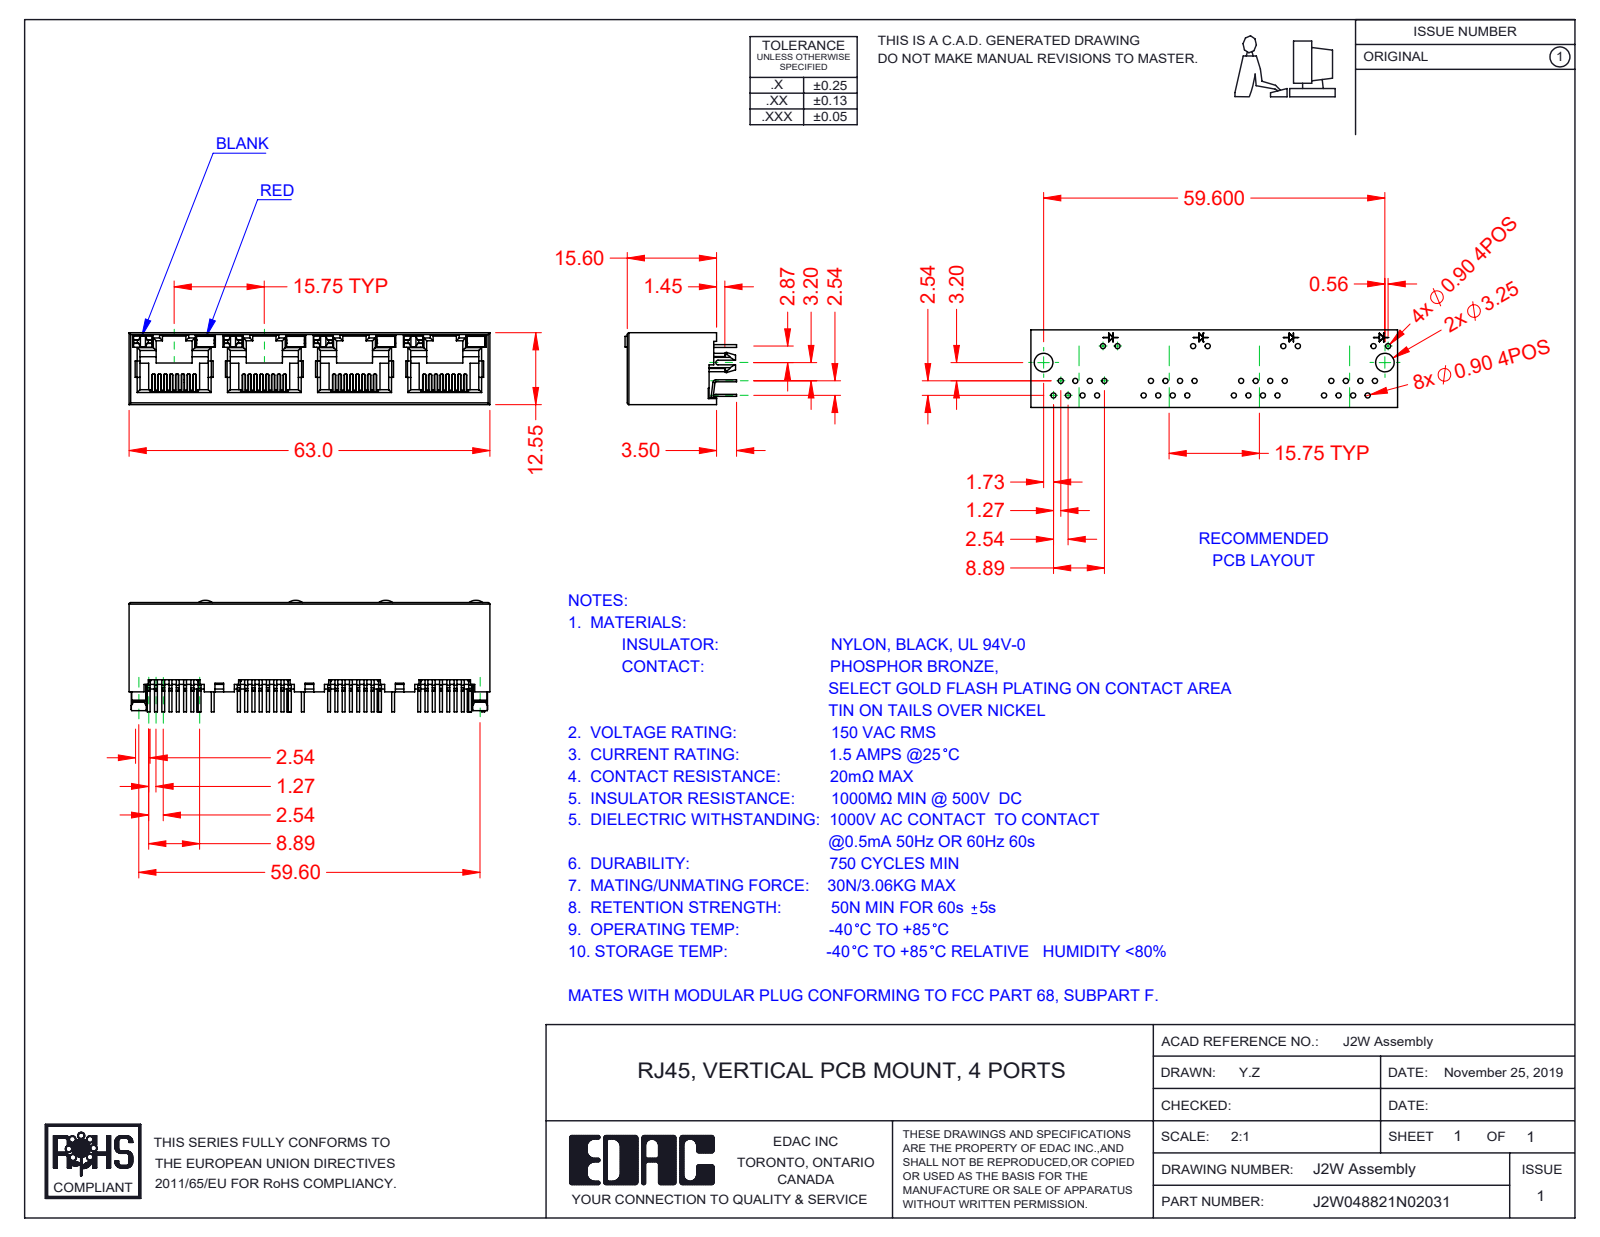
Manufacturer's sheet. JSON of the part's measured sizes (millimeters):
{"part_name": "2W Insulator; 2W Contact Lock; 2W LED RH_2-Red; 2W LED LH_0-Blank (+2 more)", "step_written_by": "SolidWorks 2020 (CONFIG_CONTROL_DESIGN)", "units": "millimeters", "bodies": {"solids": 41, "faces": 3007, "planar": 2508, "cylindrical": 441, "other": 58}, "overall_size": [63, 19.5, 12.55], "volume_mm3": 5212, "surface_area_mm2": 12695, "partial_cylinders_radius": [[0.15, 64], [0.2, 29], [0.5, 28], [0.3, 14], [0.45, 8], [2, 4], [0.25, 2], [1.5, 2]], "face_to_face_distances": [12.55, 11.9, 0.65, 15.75, 0.36, 1.5, 0.78, 0.6, 11.3, 31.5]}
